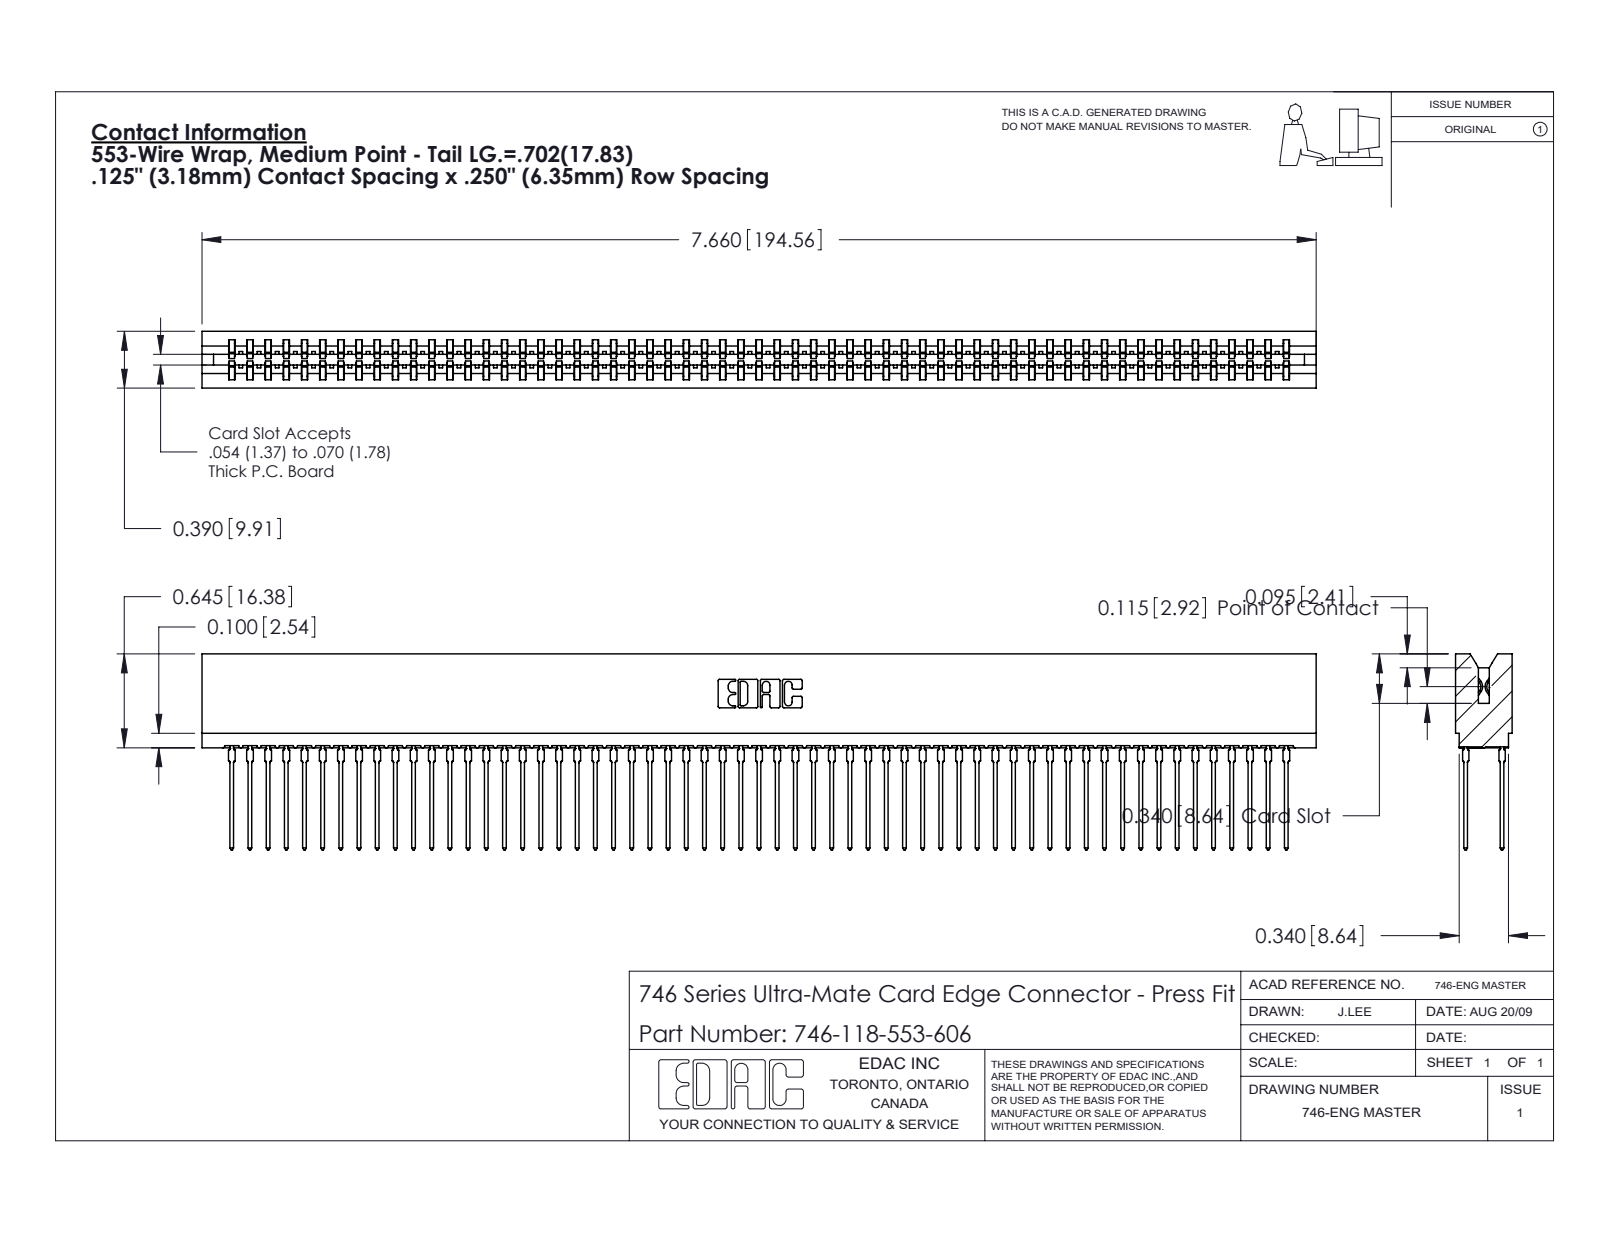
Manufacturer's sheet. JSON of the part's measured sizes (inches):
{"part_name": "746-118-553-606; 746 Part_.340 Slot Depth - 06; 746-292-001_553", "step_written_by": "SolidWorks 2020 (CONFIG_CONTROL_DESIGN)", "units": "inches", "bodies": {"solids": 119, "faces": 10659, "planar": 5484, "cylindrical": 2107, "other": 3068}, "overall_size": [7.66, 1.346, 0.39], "volume_in3": 1.391, "surface_area_in2": 56.09, "partial_cylinders_radius": [[0.021, 236], [0.015, 60], [0.01, 22], [0.005, 8], [0.011, 8], [0.007, 6], [0.031, 6], [0.026, 3]], "face_to_face_distances": [0.057, 0.333, 0.025, 0.307, 0.25, 0.39, 0.083, 0.275, 0.225, 0.015]}
